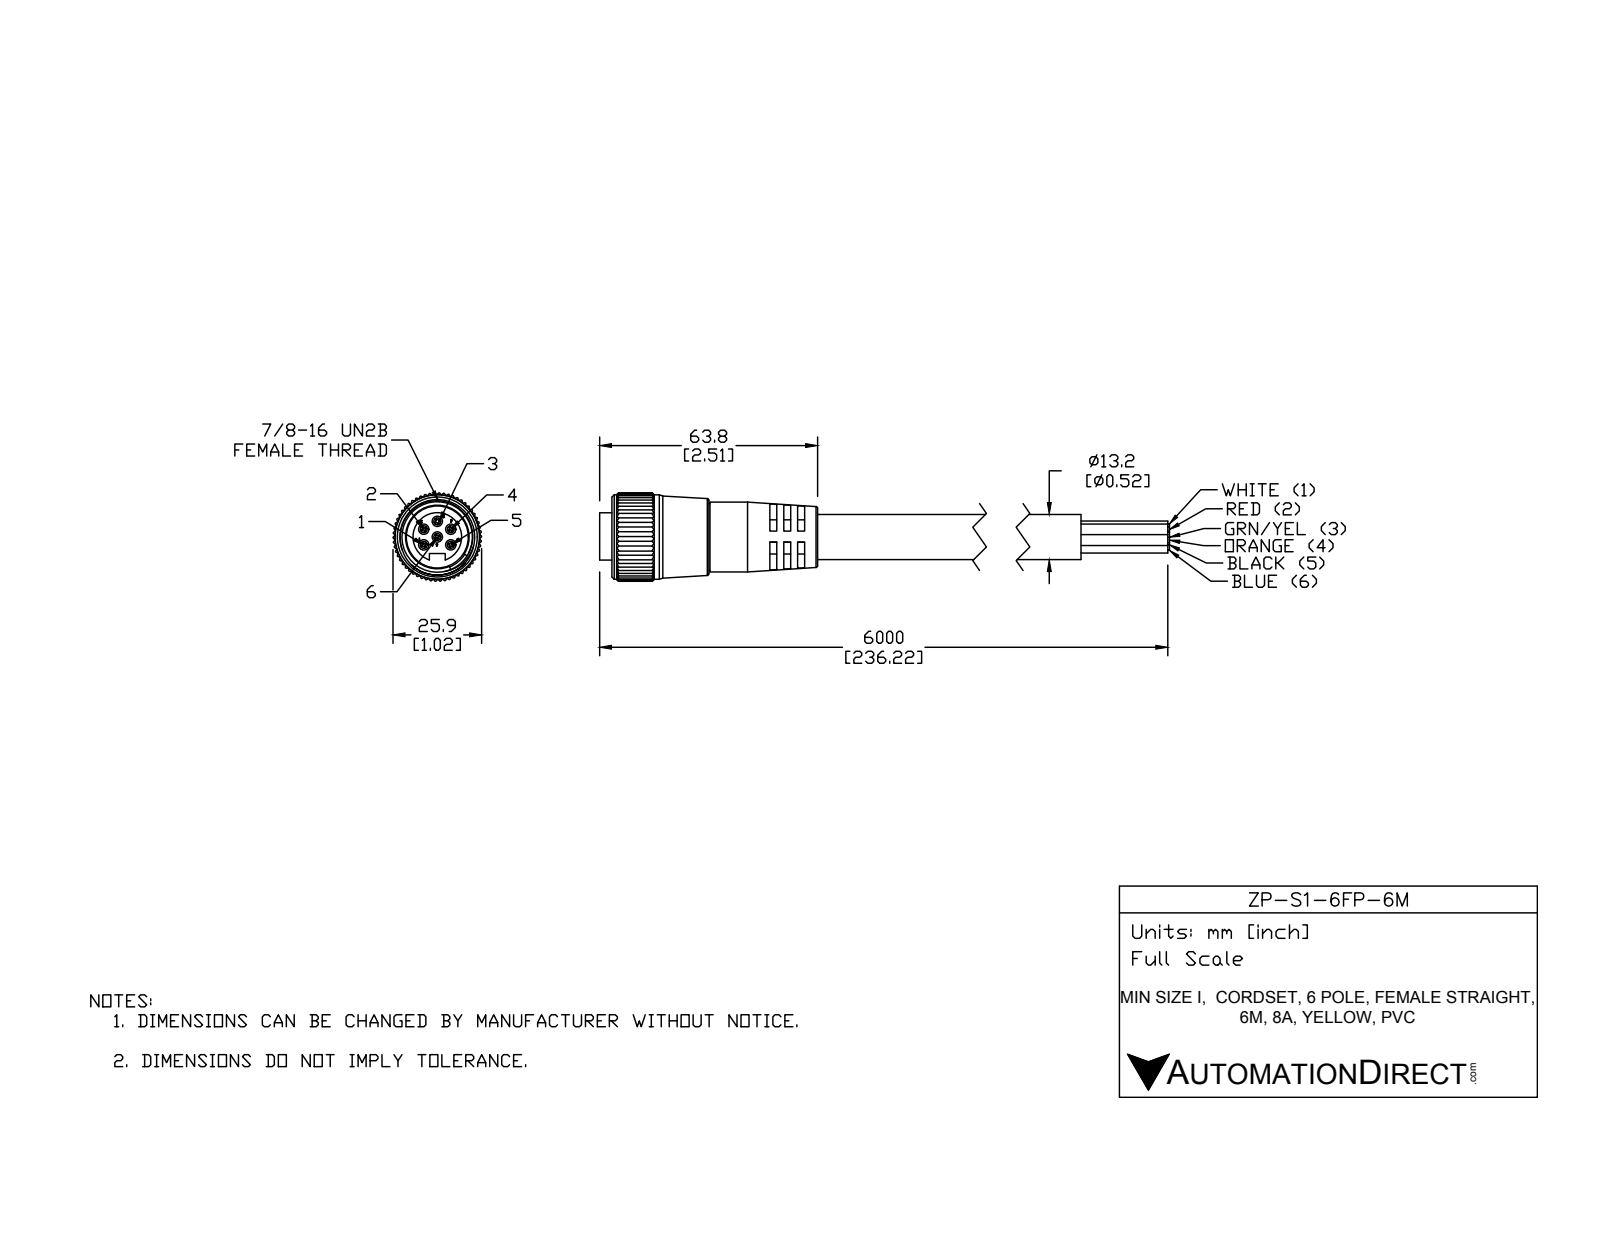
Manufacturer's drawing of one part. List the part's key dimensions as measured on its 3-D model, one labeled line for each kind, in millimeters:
Part name (STEP PRODUCT): ZP-S1-6FP-6M
STEP written by: SolidWorks 2015 (AUTOMOTIVE_DESIGN)
Units: millimetres
Bodies: 2 solids, 593 faces (222 planar, 312 cylindrical, 59 other)
Overall size (bounding box): 110.36 × 52.91 × 25.84
Volume: 31 008 mm³ · Surface area: 12 592 mm²
Round holes (diameter × count): ⌀3.05 ×6, ⌀18.14 ×1, ⌀20.58 ×1, ⌀21 ×1
Round bosses / shafts (diameter × count): ⌀13.21 ×2, ⌀24.68 ×1, ⌀20.4 ×1, ⌀19.5 ×1, ⌀14.22 ×1
Partial cylindrical surfaces — rounded edges, fillets, slot ends (radius × count): R0.25 ×165, R5.25 ×1, R12.93 ×1
Main face-to-face distances: 4.03, 2, 2.03, 6.03, 8.06, 6.06, 21.13, 23.13, 25.16, 27.16
Hole centre spacings: 4.57, 7.92, 4.58, 9.15
